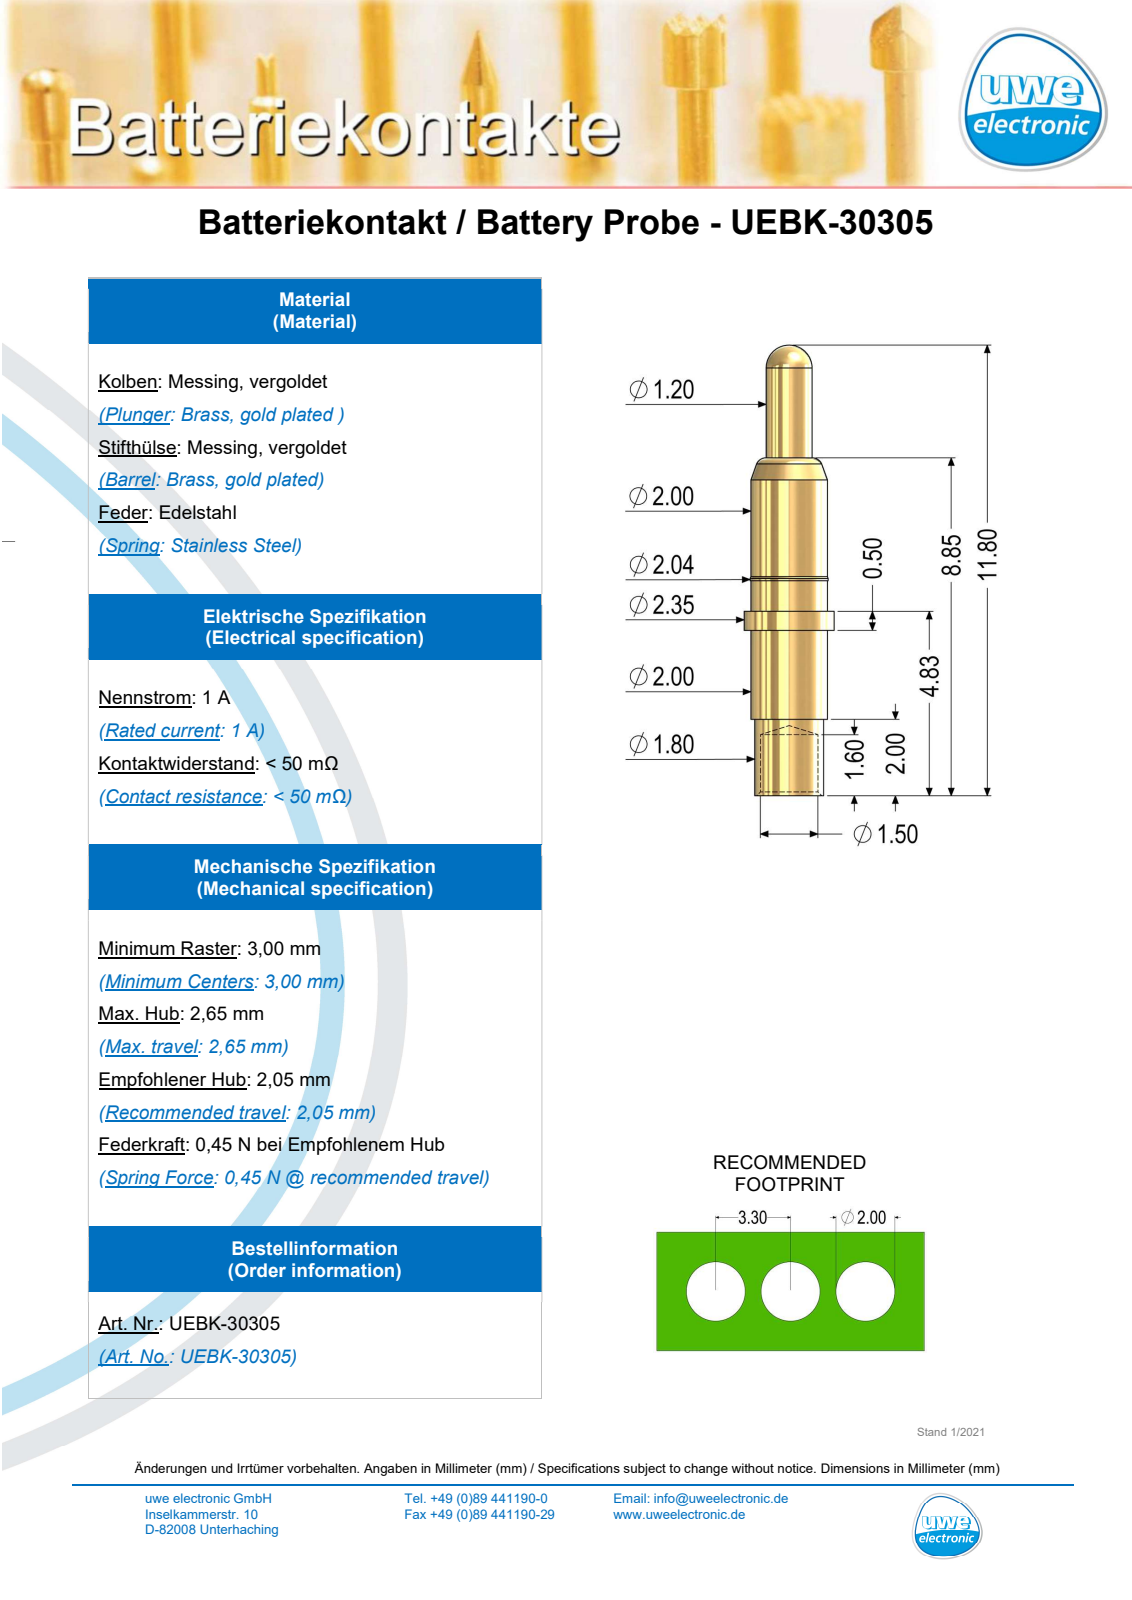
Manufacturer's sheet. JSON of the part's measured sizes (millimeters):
{"part_name": "UEBK-30305_2017_09_11", "step_written_by": "SolidWorks 2017 (AUTOMOTIVE_DESIGN)", "units": "millimeters", "bodies": {"solids": 1, "faces": 33, "planar": 5, "cylindrical": 16, "other": 12}, "overall_size": [11.8, 2.35, 2.35], "volume_mm3": 27, "surface_area_mm2": 80, "round_holes": [[1.5, 1]], "round_bosses_or_shafts": [[2.35, 1], [2.04, 1], [2, 1], [1.8, 1], [1.2, 1]], "face_to_face_distances": [0.5, 2.33, 2.83, 2, 4.33, 4.83, 5.63, 3.63, 1.3, 0.8]}
